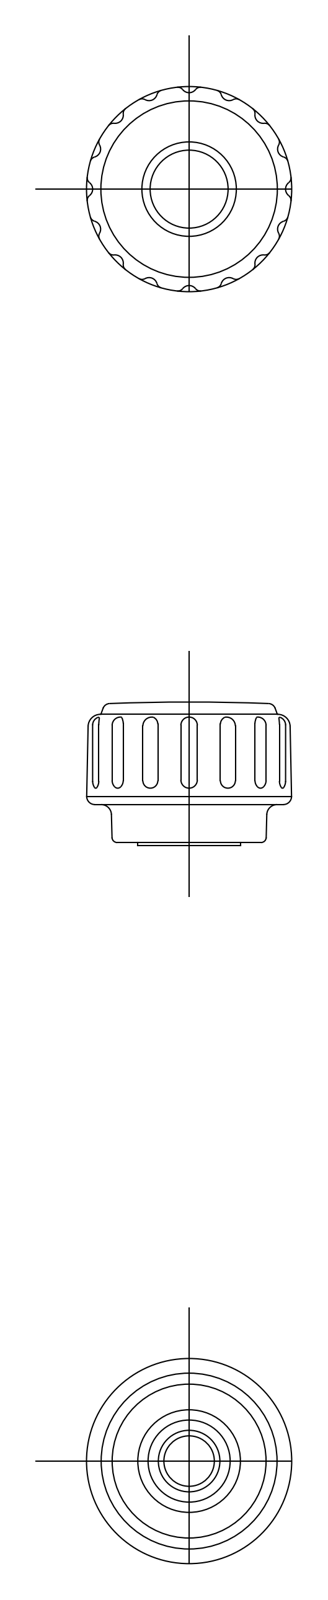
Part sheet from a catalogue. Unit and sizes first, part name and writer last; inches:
Units: inches
Overall size (bounding box): 0.792 × 0.786 × 0.549
Volume: 0.204 in³ · Surface area: 2.804 in²
Bodies: 2 solids, 67 faces (0 planar, 0 cylindrical, 67 other)
Part name (STEP PRODUCT): 67114862; 67114875
STEP written by: CADfix (AUTOMOTIVE_DESIGN)
